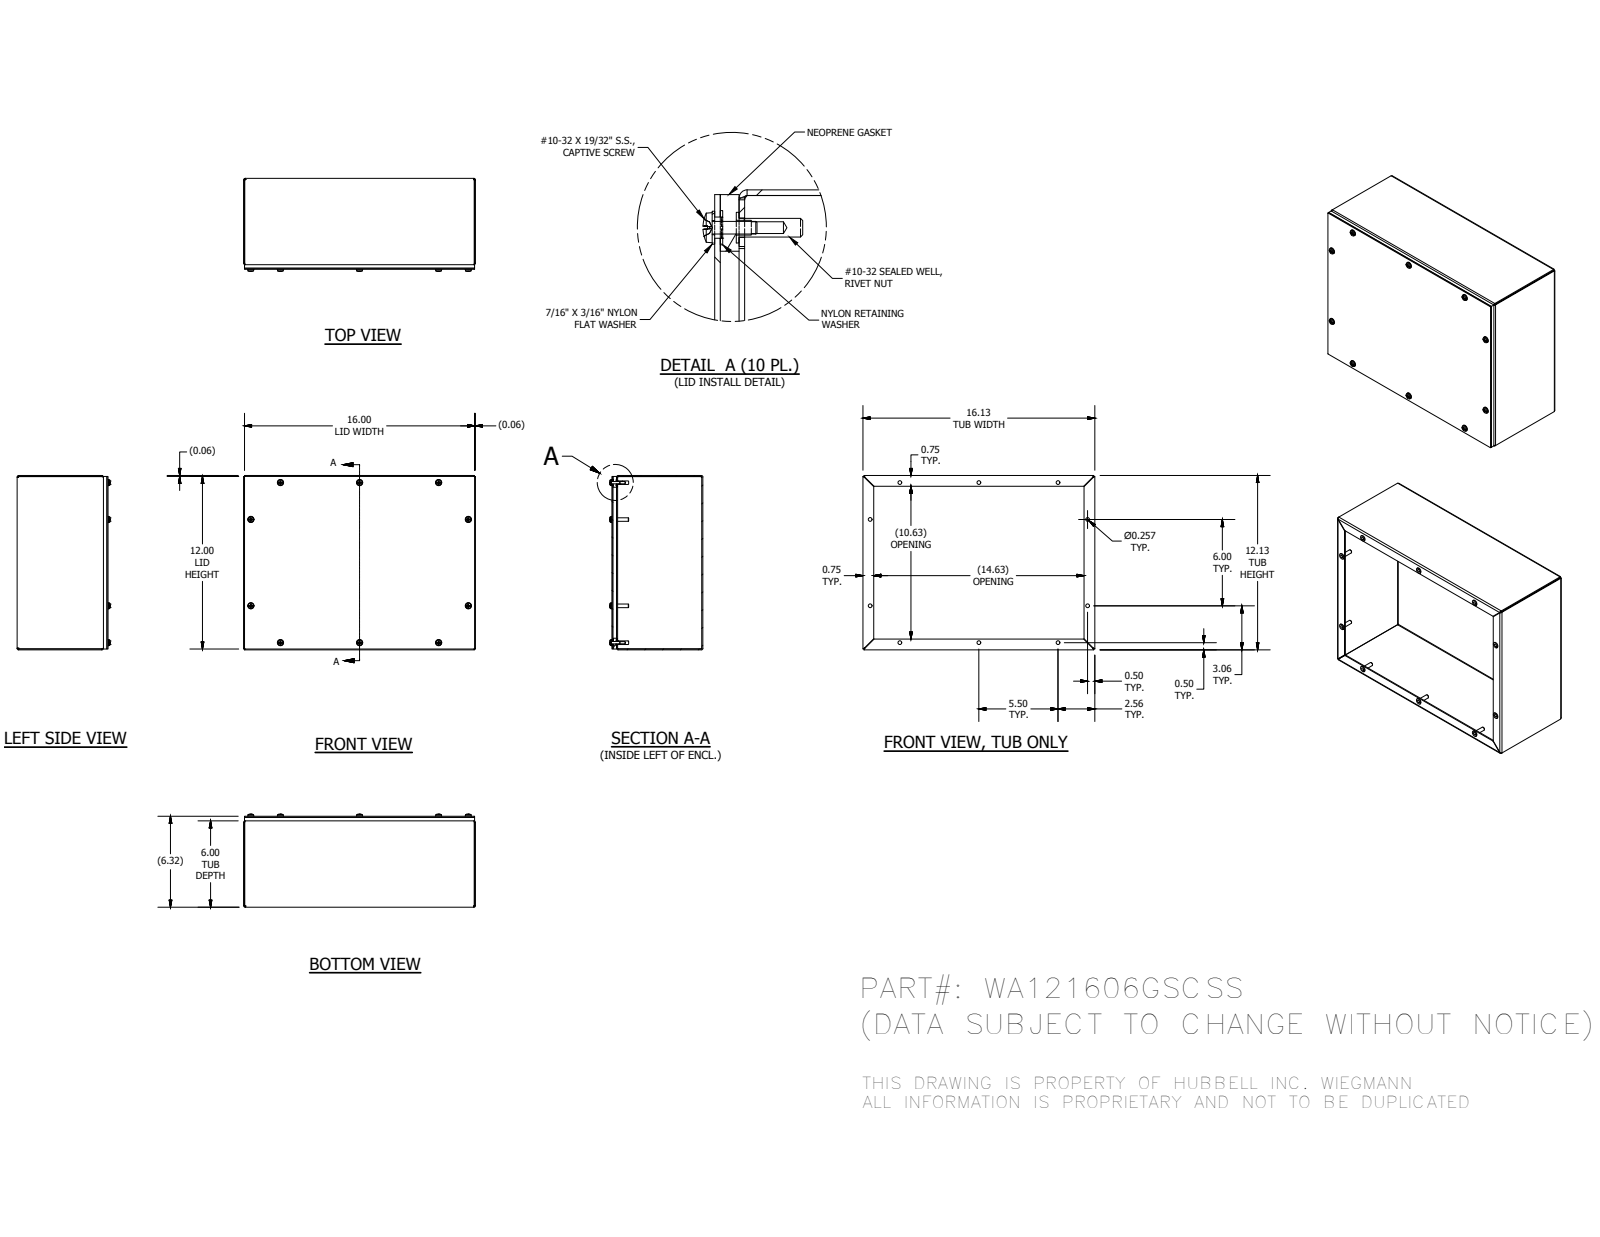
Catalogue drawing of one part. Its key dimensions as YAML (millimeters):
part_name: "WA121606GSCSSBKP; WA1216GSCSSLID; 37210; 39035 (+4 more)"
step_written_by: "Autodesk Inventor 2016 (AUTOMOTIVE_DESIGN)"
units: millimeters
bodies: {solids: 43, faces: 902, planar: 494, cylindrical: 182, other: 226}
overall_size: [409.57, 307.98, 164.56]
volume: 1083000
surface_area: 1062000
round_holes:
  - {diameter: 3.96, count: 10}
  - {diameter: 4.78, count: 10}
  - {diameter: 4.98, count: 10}
  - {diameter: 6.53, count: 10}
  - {diameter: 7.06, count: 10}
  - {diameter: 7.14, count: 10}
round_bosses_or_shafts:
  - {diameter: 11.51, count: 10}
  - {diameter: 11.11, count: 10}
  - {diameter: 10.31, count: 10}
  - {diameter: 6.3, count: 10}
  - {diameter: 4.25, count: 10}
partial_cylinders:
  - {radius: 0.79, count: 12}
  - {radius: 2.27, count: 10}
  - {radius: 1.78, count: 8}
  - {radius: 2.67, count: 8}
face_to_face_distances: [1.88, 158.75, 156.87, 160.63, 306.1, 407.7, 150.52, 8.23, 307.98, 304.22]
hole_center_spacings: [83.55, 139.7, 202.82, 223.71, 290.17, 315.23, 338.11, 396.72]
